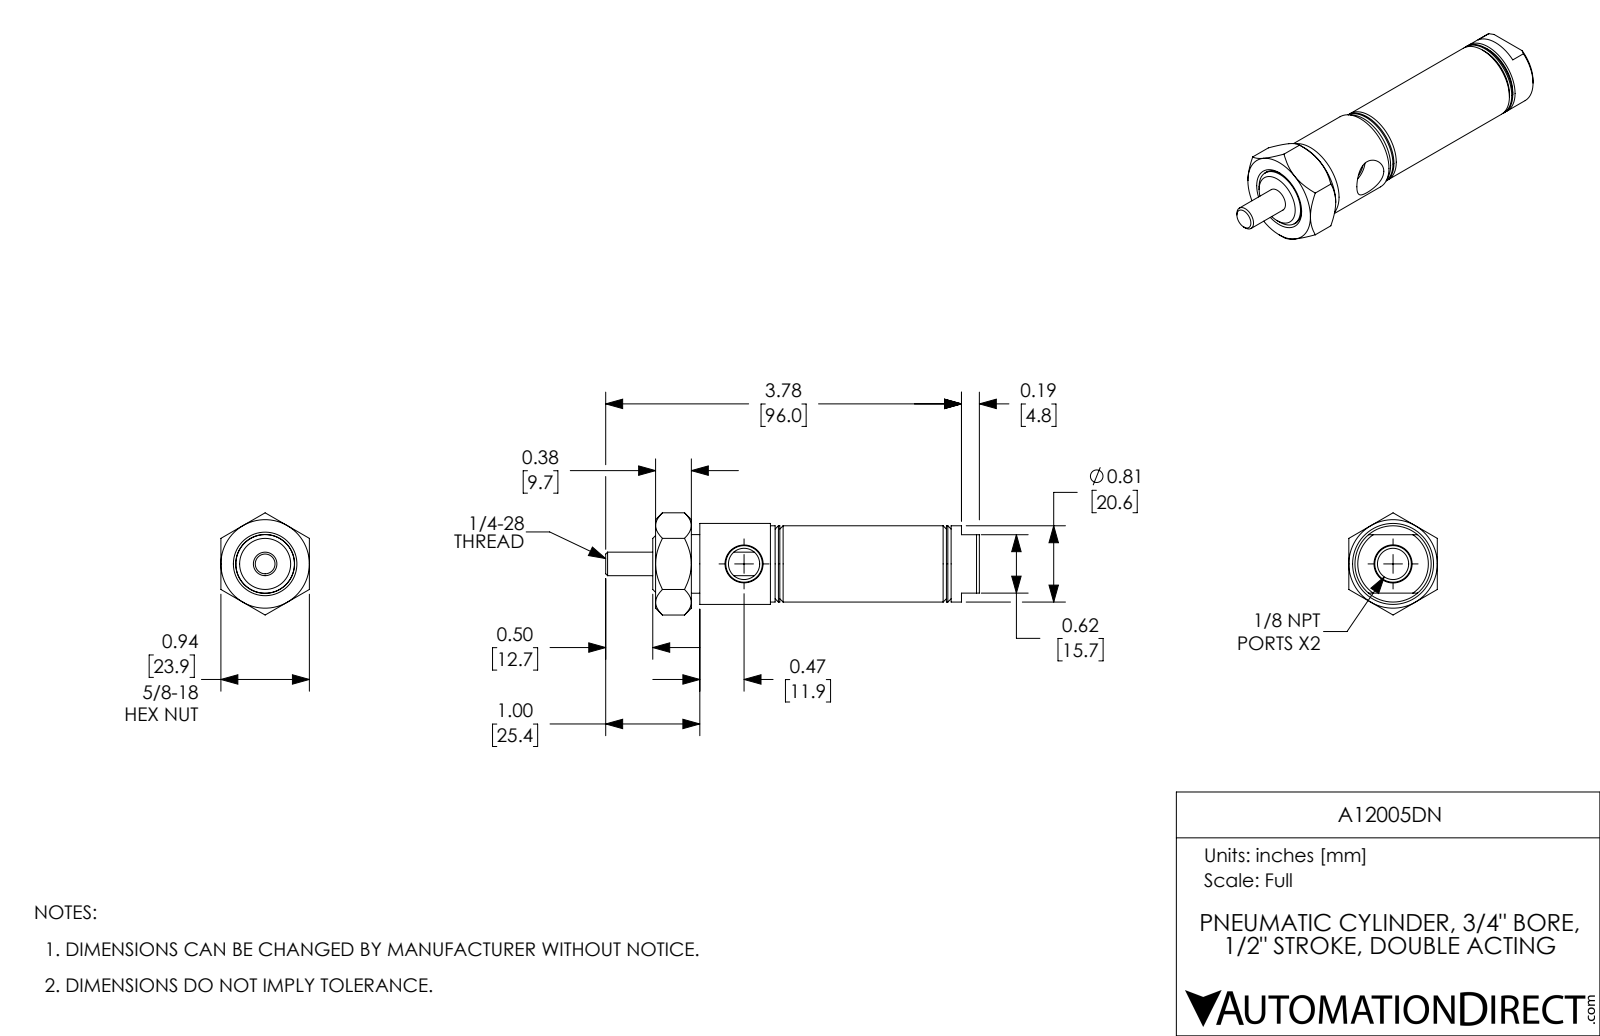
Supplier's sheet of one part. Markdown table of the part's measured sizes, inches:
| quantity | value |
| --- | --- |
| part name | A12005DN_Mounting Nut_D-9; A12005DN-Rod; A12005DN-MainBody; A12005DN |
| STEP written by | SolidWorks 2017 (AUTOMOTIVE_DESIGN) |
| units | inches |
| bodies | 3 solids, 94 faces (27 planar, 28 cylindrical, 39 other) |
| overall size | 3.97 × 1.085 × 0.94 |
| volume | 1.574 in³ |
| surface area | 22.36 in² |
| round holes (diameter × count) | 0.332 × 2, 0.25 × 1, 0.625 × 1, 0.75 × 1 |
| round bosses / shafts (diameter × count) | 0.86 × 1, 0.81 × 1, 0.623 × 1 |
| main face-to-face distances | 0.5, 1.985, 1.485, 0.94, 0.985, 1, 2.075, 1.575, 1.075, 2.455 |
